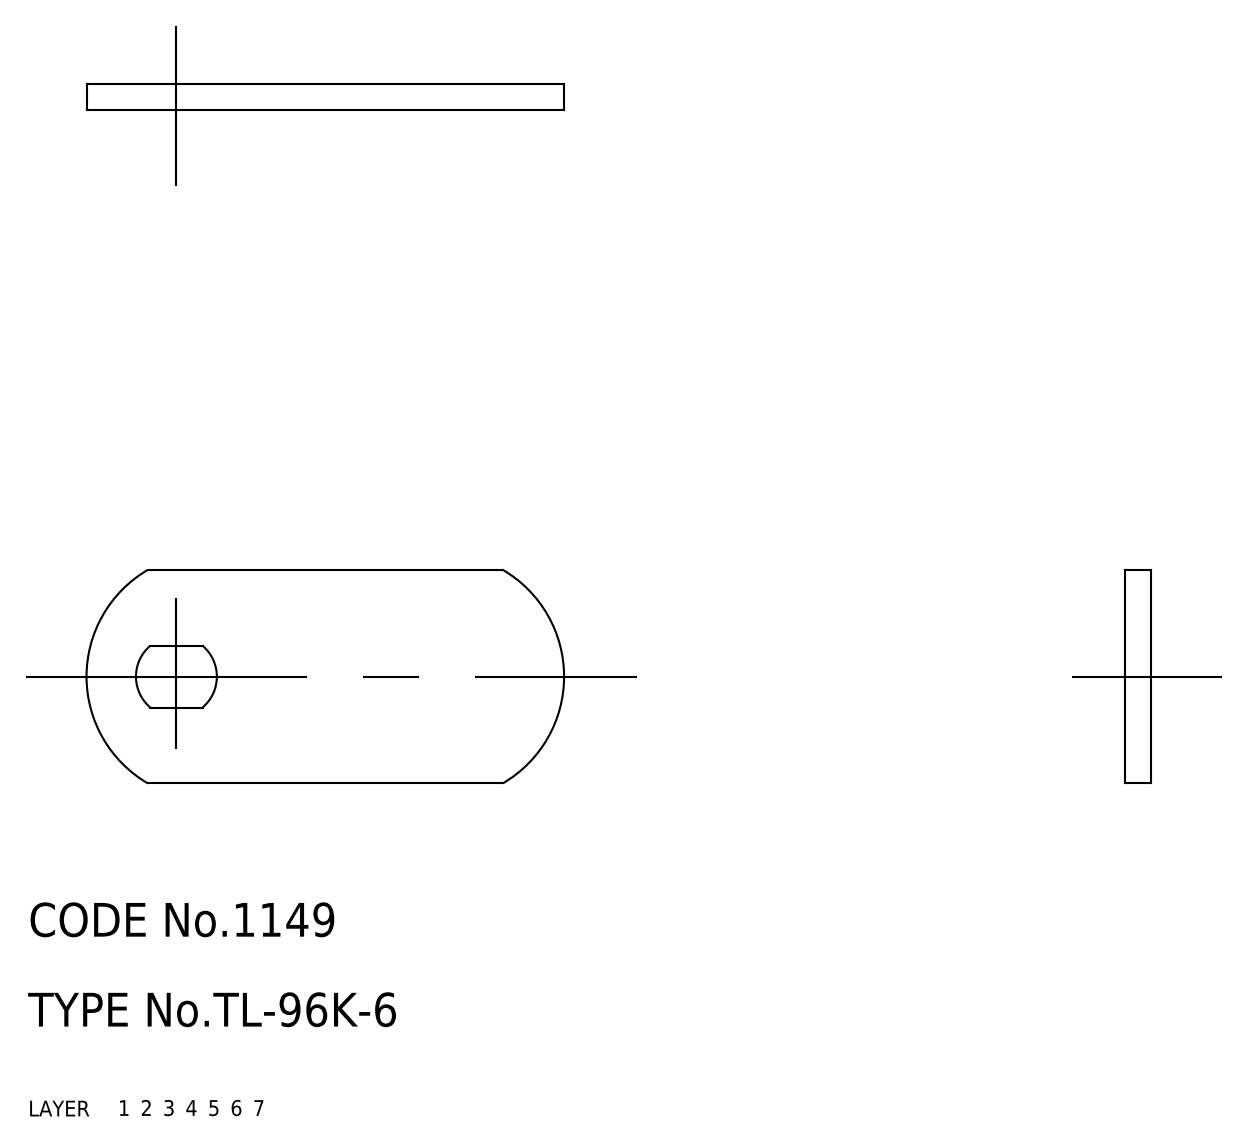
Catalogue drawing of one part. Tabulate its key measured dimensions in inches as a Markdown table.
| quantity | value |
| --- | --- |
| part name | cam |
| STEP written by | CADfix (AUTOMOTIVE_DESIGN) |
| units | inches |
| bodies | 1 solid, 10 faces (0 planar, 0 cylindrical, 10 other) |
| overall size | 1.673 × 0.748 × 0.091 |
| volume | 0.1 in³ |
| surface area | 2.674 in² |
